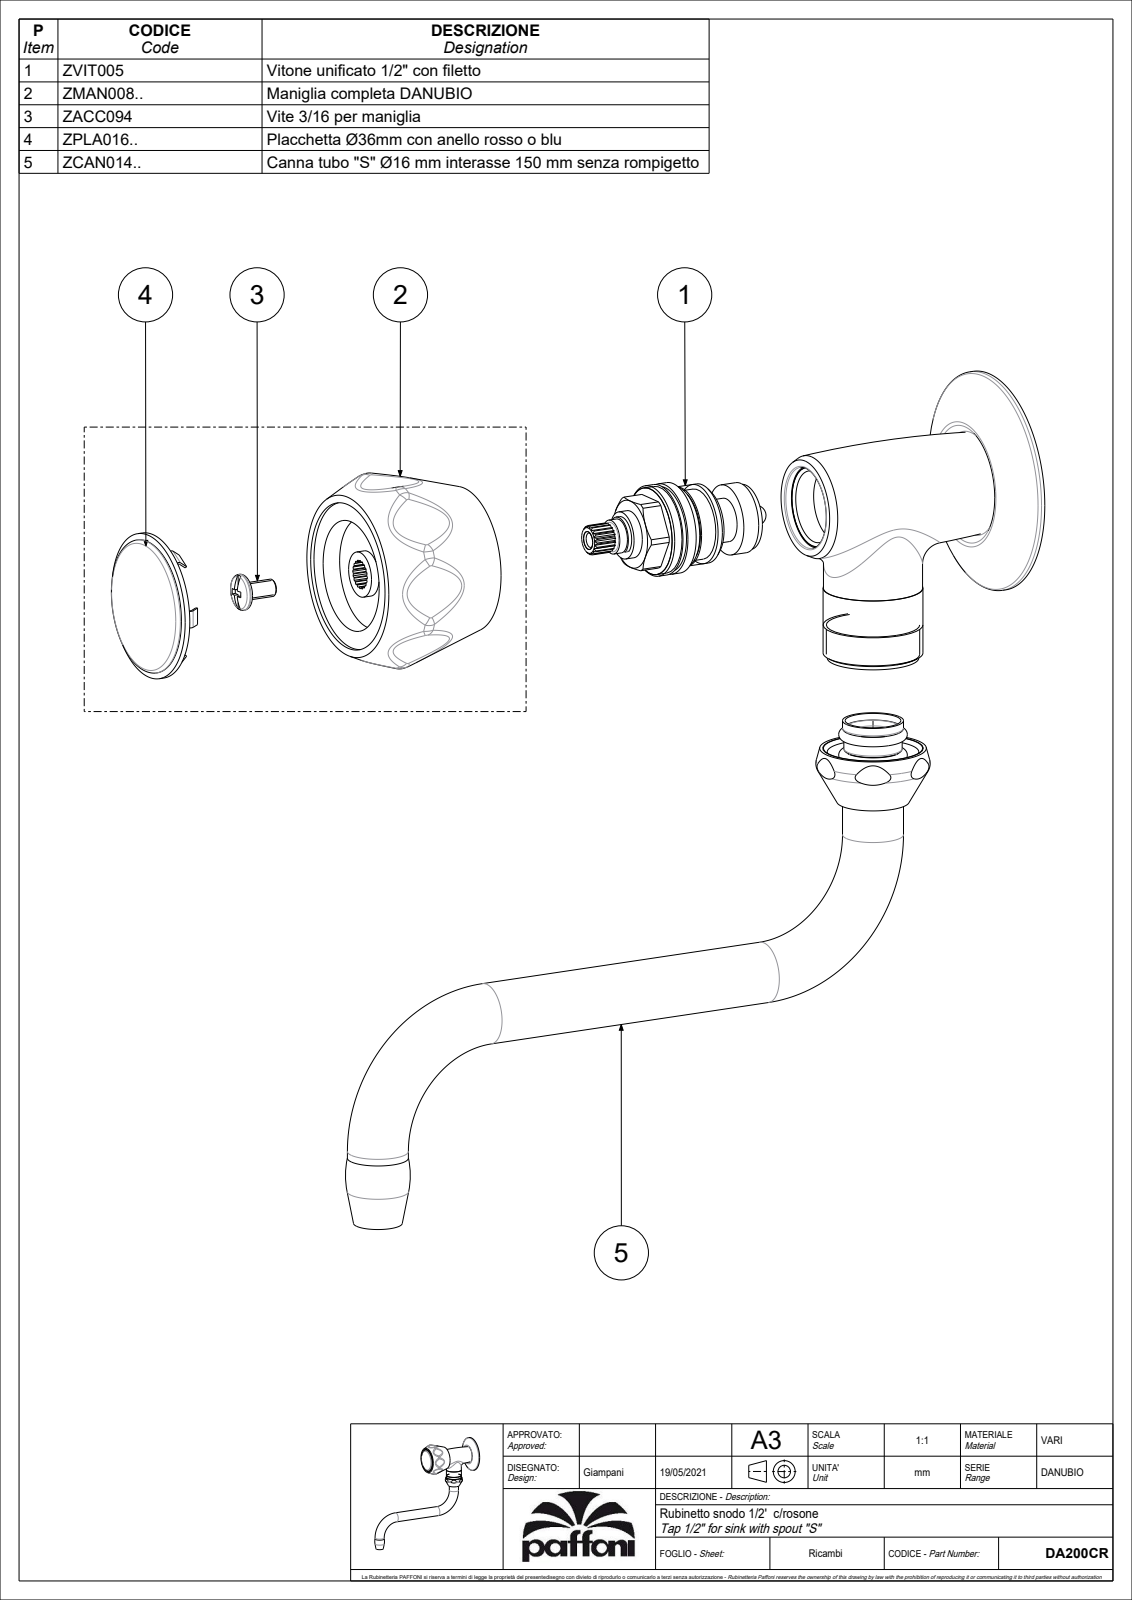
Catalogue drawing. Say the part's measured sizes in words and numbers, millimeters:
The part is named "DA200CR". Its 3-D file was written by "CREO PARAMETRIC BY PTC INC, 2020044 (CONFIG_CONTROL_DESIGN)". It is 1 solid with 129 faces: 15 planar, 24 cylindrical and 90 other. Overall it measures 200.5 by 176 by 58 millimeters. Its volume is 171 937 cubic millimeters and its surface area 31 676 square millimeters. Round bosses or shafts: 3 of diameter 16, 1 of diameter 58, 1 of diameter 38.5, 1 of diameter 26.2, 1 of diameter 26, 1 of diameter 21. Partial cylindrical surfaces (rounded edges, fillets, slot ends): 8 of radius 21.31. The main face-to-face distances are 54.1, 89.4, 35.3, 6.7, 60.8, 96.1, 96.5, 89.8, 35.7, 0.4.
